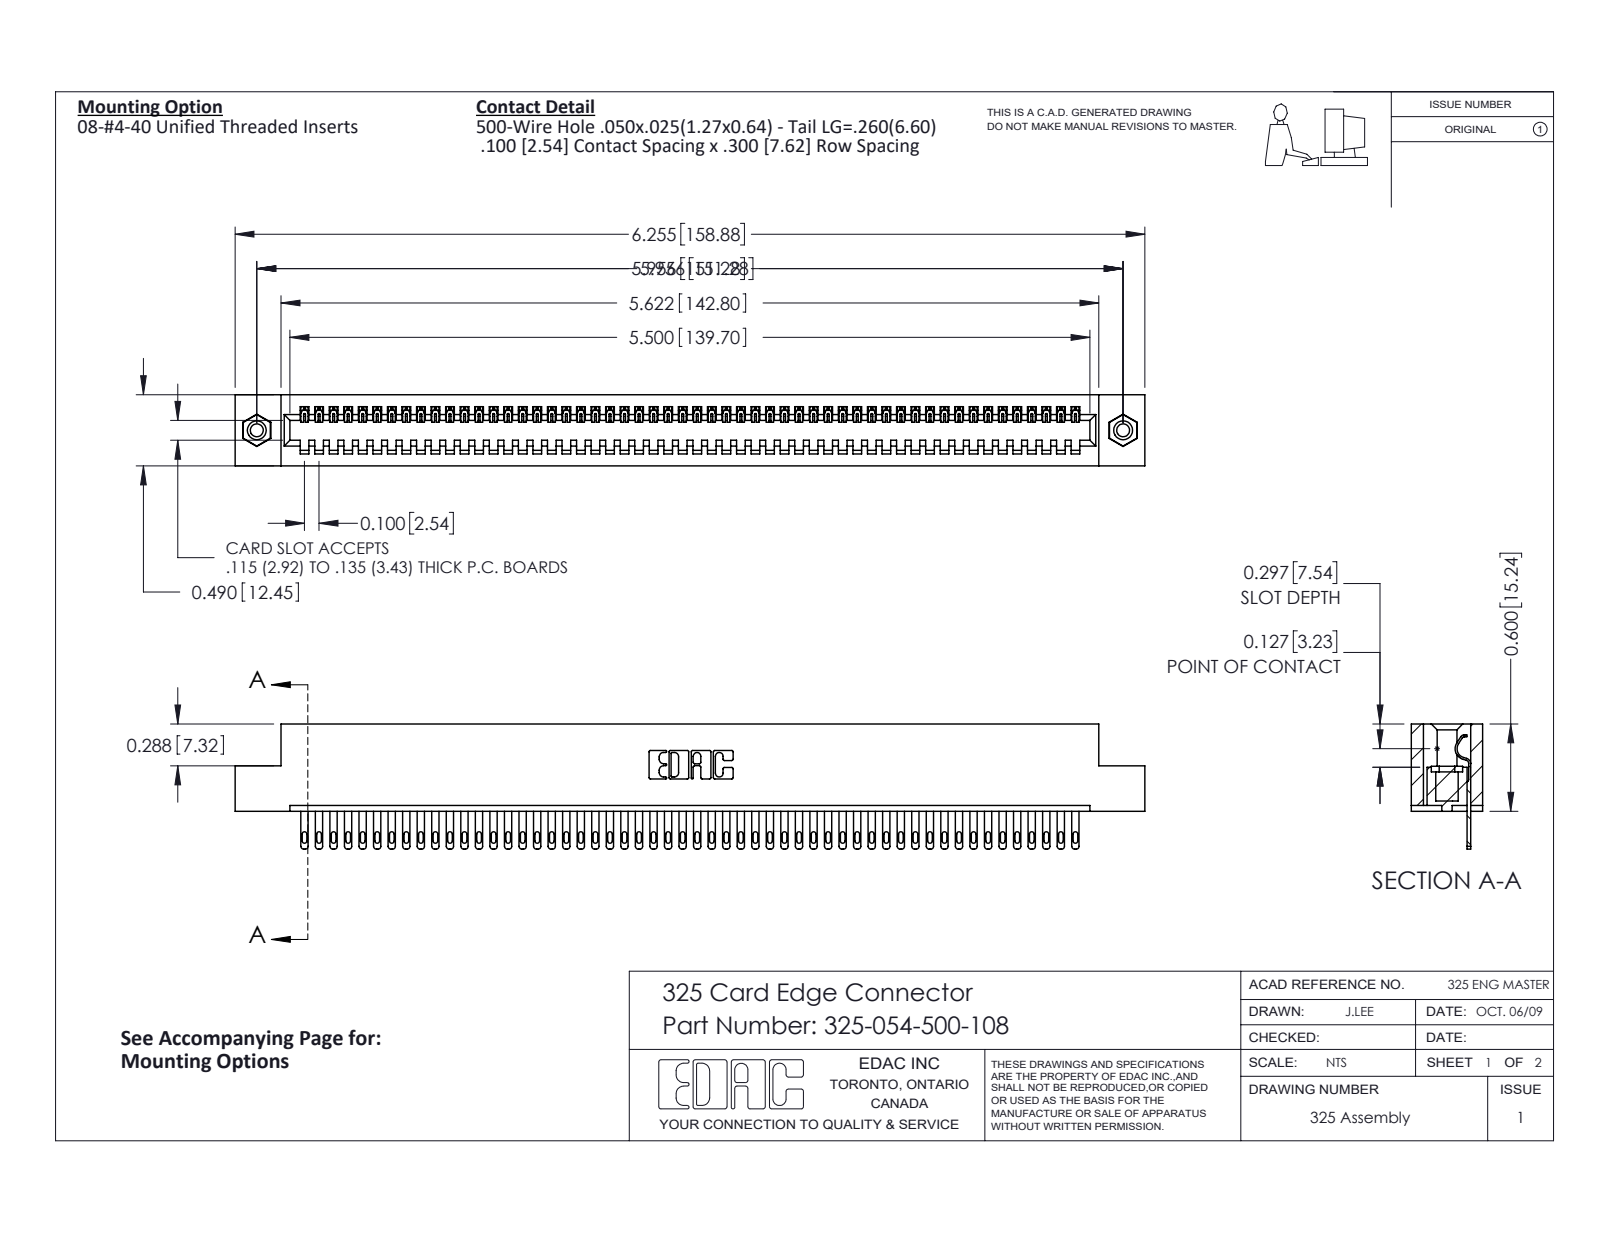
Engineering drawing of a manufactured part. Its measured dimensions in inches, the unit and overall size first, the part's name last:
Units: inches
Overall size (bounding box): 6.255 × 0.86 × 0.49
Round holes (diameter × count): ⌀0.089 ×2, ⌀0.125 ×2, ⌀0.16 ×2
Round bosses / shafts (diameter × count): ⌀0.155 ×2
Partial cylindrical surfaces — rounded edges, fillets, slot ends (radius × count): R0.006 ×108, R0.016 ×108, R0.02 ×108, R0.01 ×22, R0.007 ×6, R0.031 ×6, R0.026 ×3, R0.014 ×1
Main face-to-face distances: 0.083, 0.407, 0.3, 0.49, 0.107, 0.383, 0.025, 0.325, 0.56, 0.263
Hole centre spacings: 5.956
Volume: 1.238 in³ · Surface area: 34.9 in²
Bodies: 57 solids, 3090 faces (2046 planar, 1028 cylindrical, 16 other)
Part name (STEP PRODUCT): 345-250-001_345-250-003-102; 325-054-500-108; 325 Part_TI; 325-292-001_325-293-100
STEP written by: SolidWorks 2016 (CONFIG_CONTROL_DESIGN)
